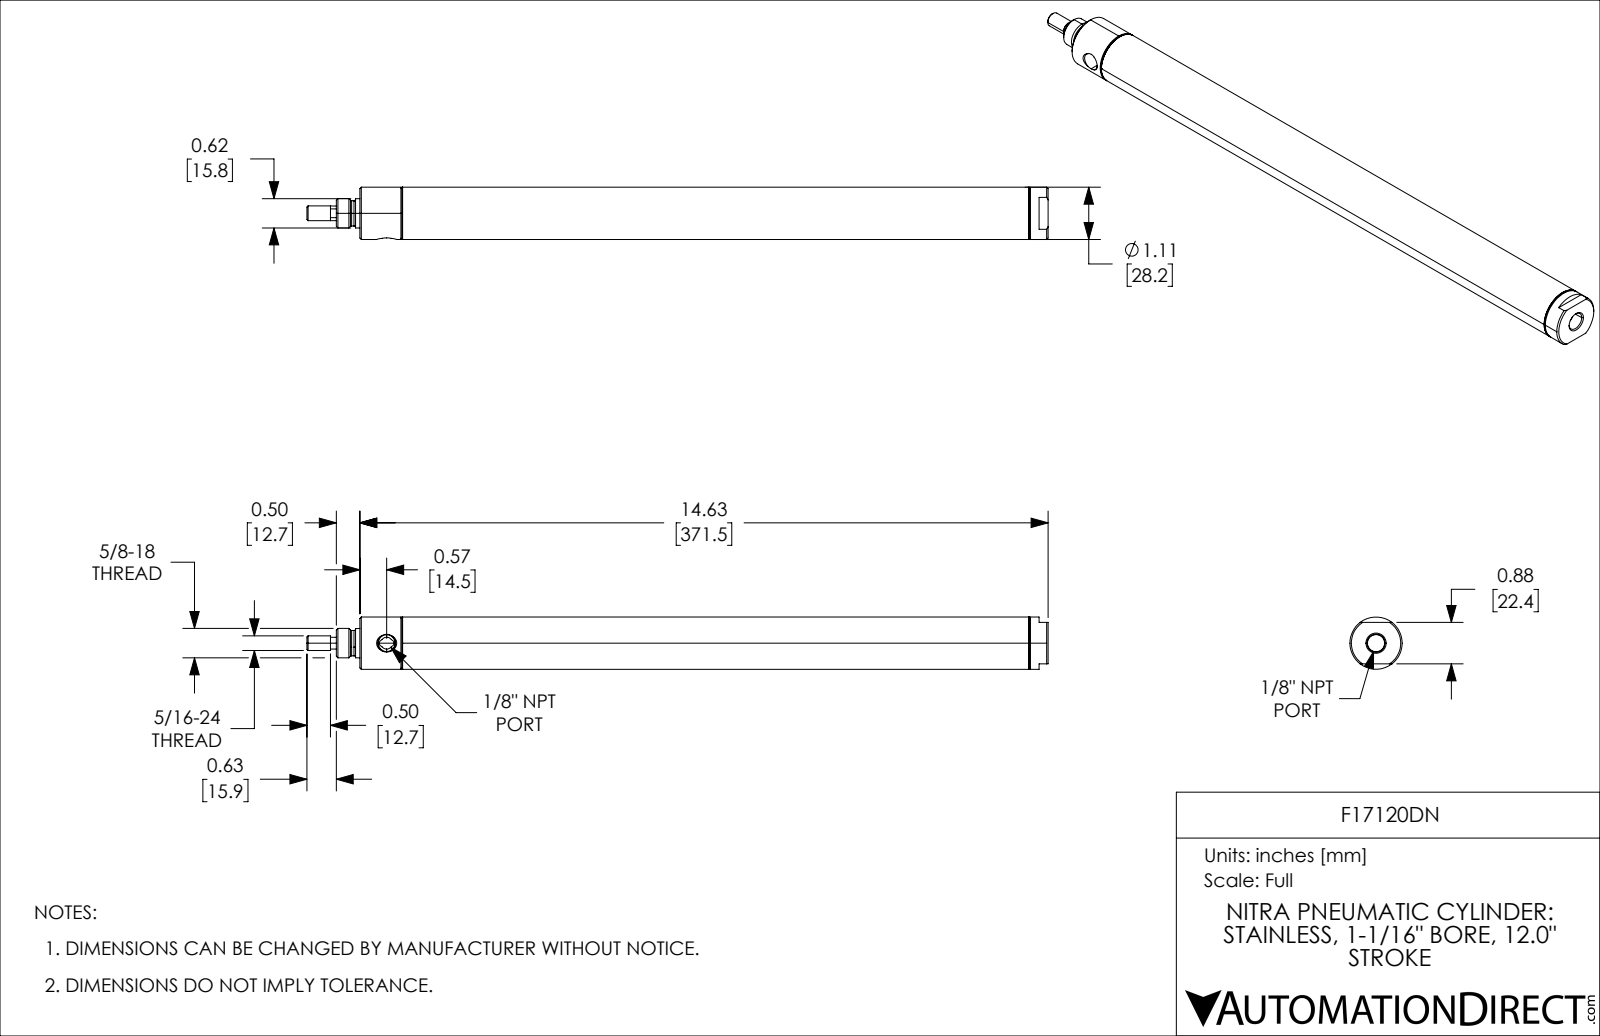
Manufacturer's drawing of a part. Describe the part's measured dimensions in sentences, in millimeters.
The part is named "F17120DN_5; F17120DN_7; F17120DN; F17120DN_3 (+1 more)". Its 3-D file was written by "SolidWorks 2021 (CONFIG_CONTROL_DESIGN)". It is 4 solids with 125 faces: 25 planar, 44 cylindrical and 56 other. Overall it measures 400.05 by 28.19 by 28.19 millimeters. Its volume is 68 521 cubic millimeters and its surface area 80 444 square millimeters. Round holes: 1 of diameter 8.53, 1 of diameter 9.25, 1 of diameter 19.05, 1 of diameter 25.7. Round bosses or shafts: 1 of diameter 28.19, 1 of diameter 27.23, 1 of diameter 15.88, 1 of diameter 15.81, 1 of diameter 13.68, 1 of diameter 7.94, 1 of diameter 7.92. Partial cylindrical surfaces (rounded edges, fillets, slot ends): 1 of radius 3.17. The main face-to-face distances are 22.22, 304.8, 327.02, 342.9, 38.1, 15.88, 28.58, 333.38, 355.6, 371.48.
